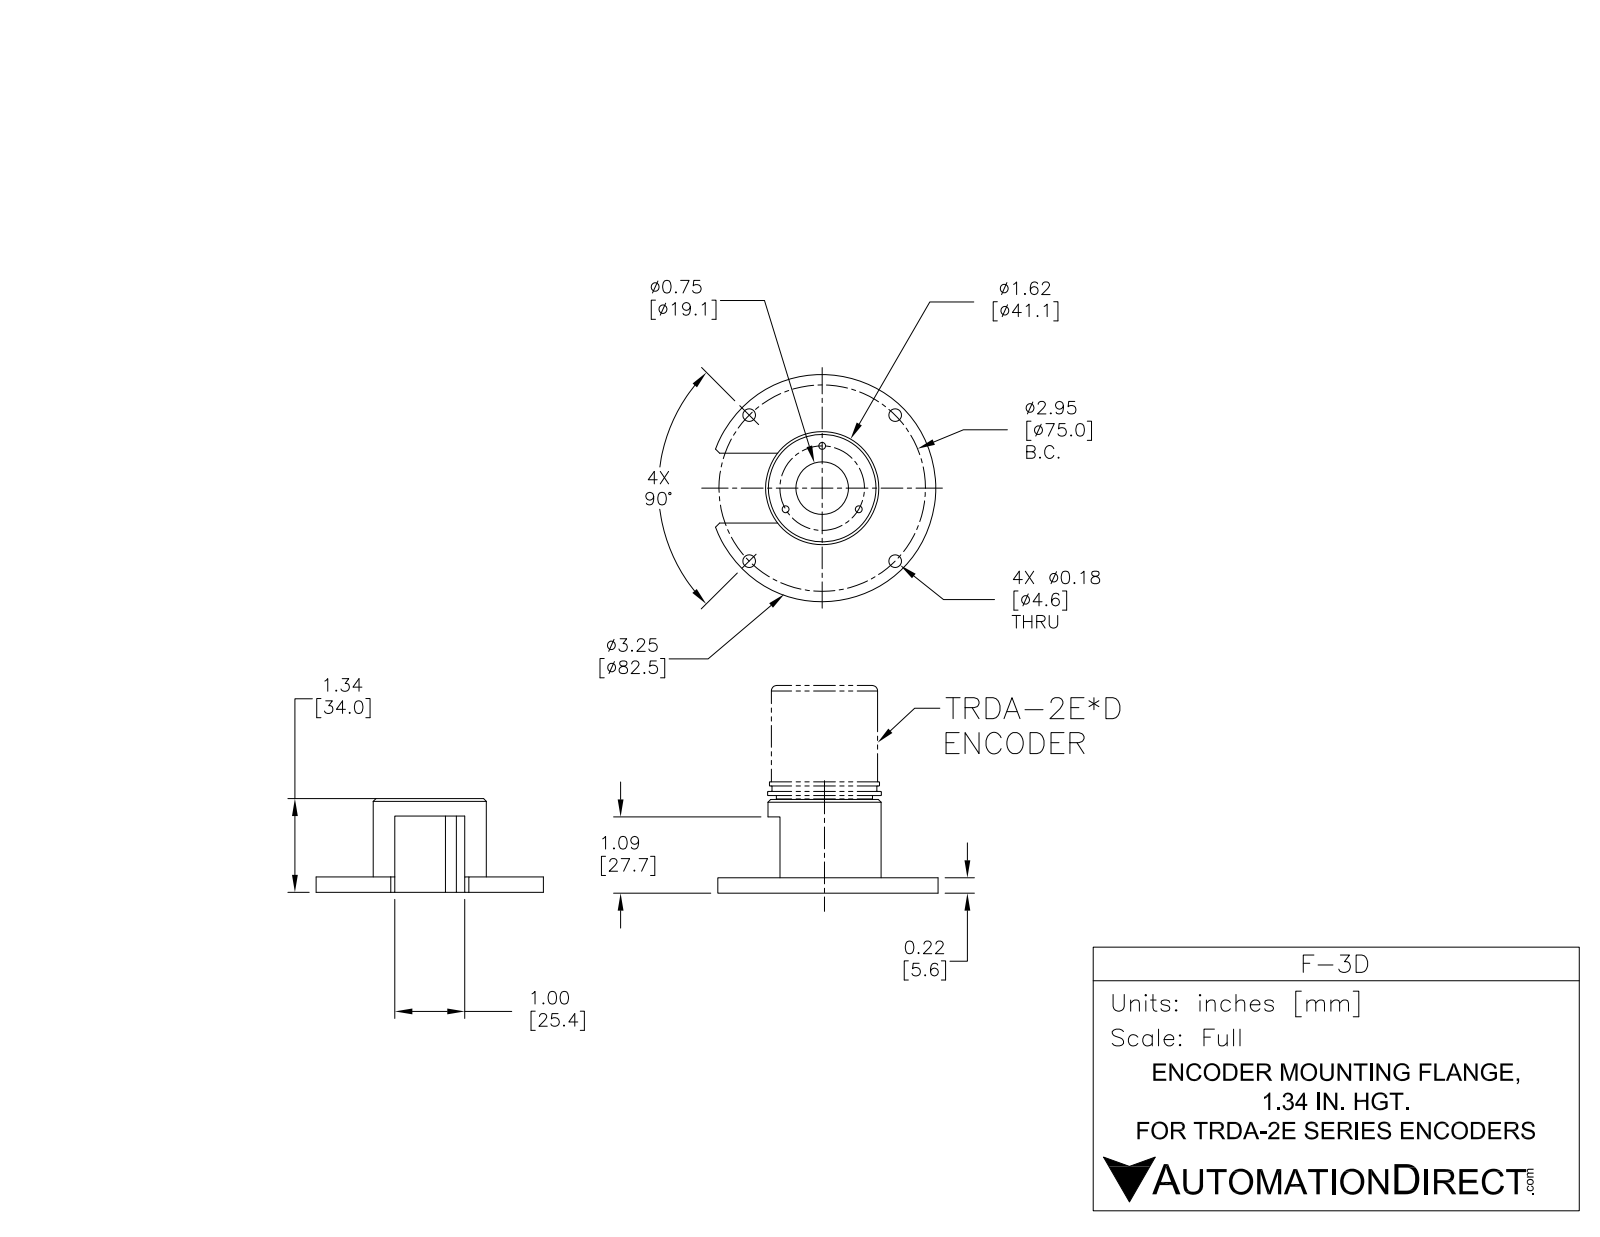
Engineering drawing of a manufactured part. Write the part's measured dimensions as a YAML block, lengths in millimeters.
part_name: "F-3D"
step_written_by: "SolidWorks 2016 (AUTOMOTIVE_DESIGN)"
units: millimeters
bodies: {solids: 1, faces: 48, planar: 12, cylindrical: 30, other: 6}
overall_size: [82.55, 80.09, 34.04]
volume: 36037
surface_area: 16784
round_holes:
  - {diameter: 4.6, count: 4}
  - {diameter: 3.2, count: 3}
  - {diameter: 5.51, count: 3}
  - {diameter: 19.05, count: 1}
  - {diameter: 30.99, count: 1}
round_bosses_or_shafts:
  - {diameter: 82.55, count: 1}
  - {diameter: 41.15, count: 1}
face_to_face_distances: [5.59, 28.45, 34.04, 25.4, 5.08, 23.37, 28.96, 6.35, 1.27, 22.1]
hole_center_spacings: [37.49, 53.02, 15.37, 26.62, 23, 28.76, 36.65, 44.05]
